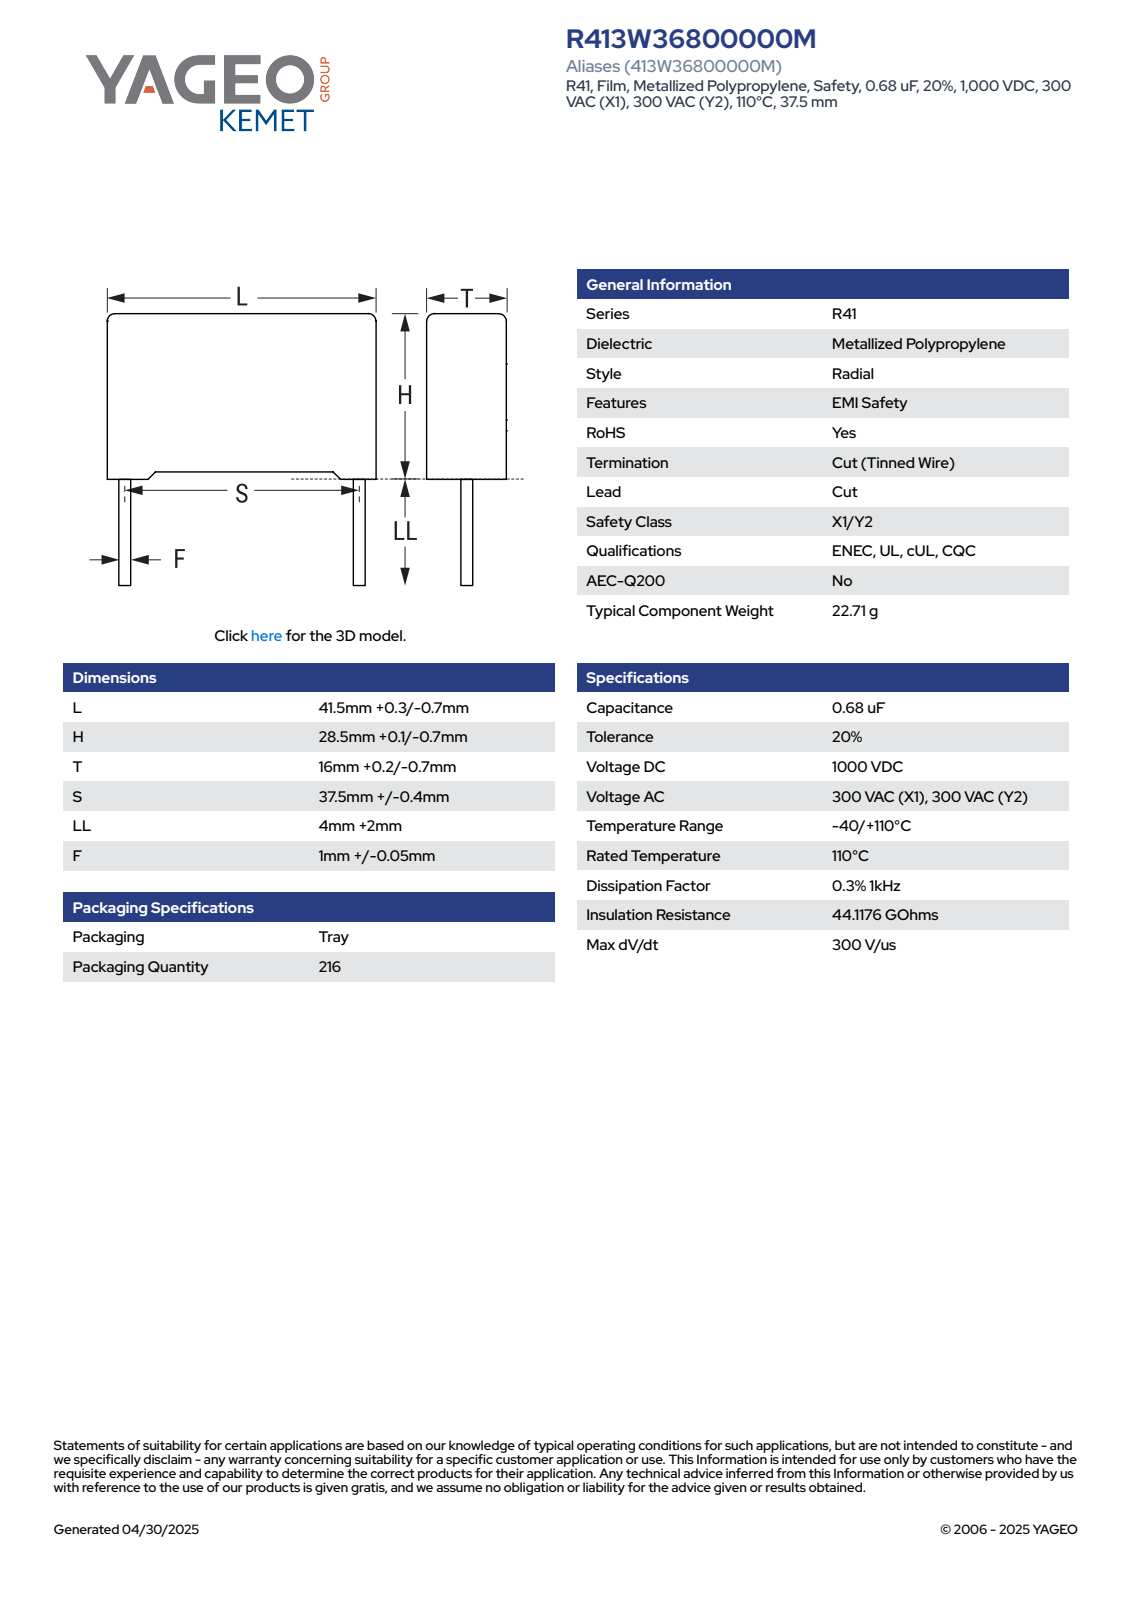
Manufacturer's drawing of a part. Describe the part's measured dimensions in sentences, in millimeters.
The part is named "CFR_RB2_41.5X28.5X16_L41.8H28.6T16.2S37.5LL6F1.05". Its 3-D file was written by "SolidWorks 2021 (AUTOMOTIVE_DESIGN)". It is 4 solids with 85 faces: 77 planar, 8 cylindrical and 0 other. Overall it measures 41.8 by 34.6 by 16.2 millimeters. Its volume is 18 786 cubic millimeters and its surface area 4 789 square millimeters. Round bosses or shafts: 2 of diameter 1.05. Partial cylindrical surfaces (rounded edges, fillets, slot ends): 4 of radius 0.5. The main face-to-face distances are 16.2, 27.61, 41.8, 27.85, 0.75, 0.99, 28.6, 16.21, 1.39, 40.41.
